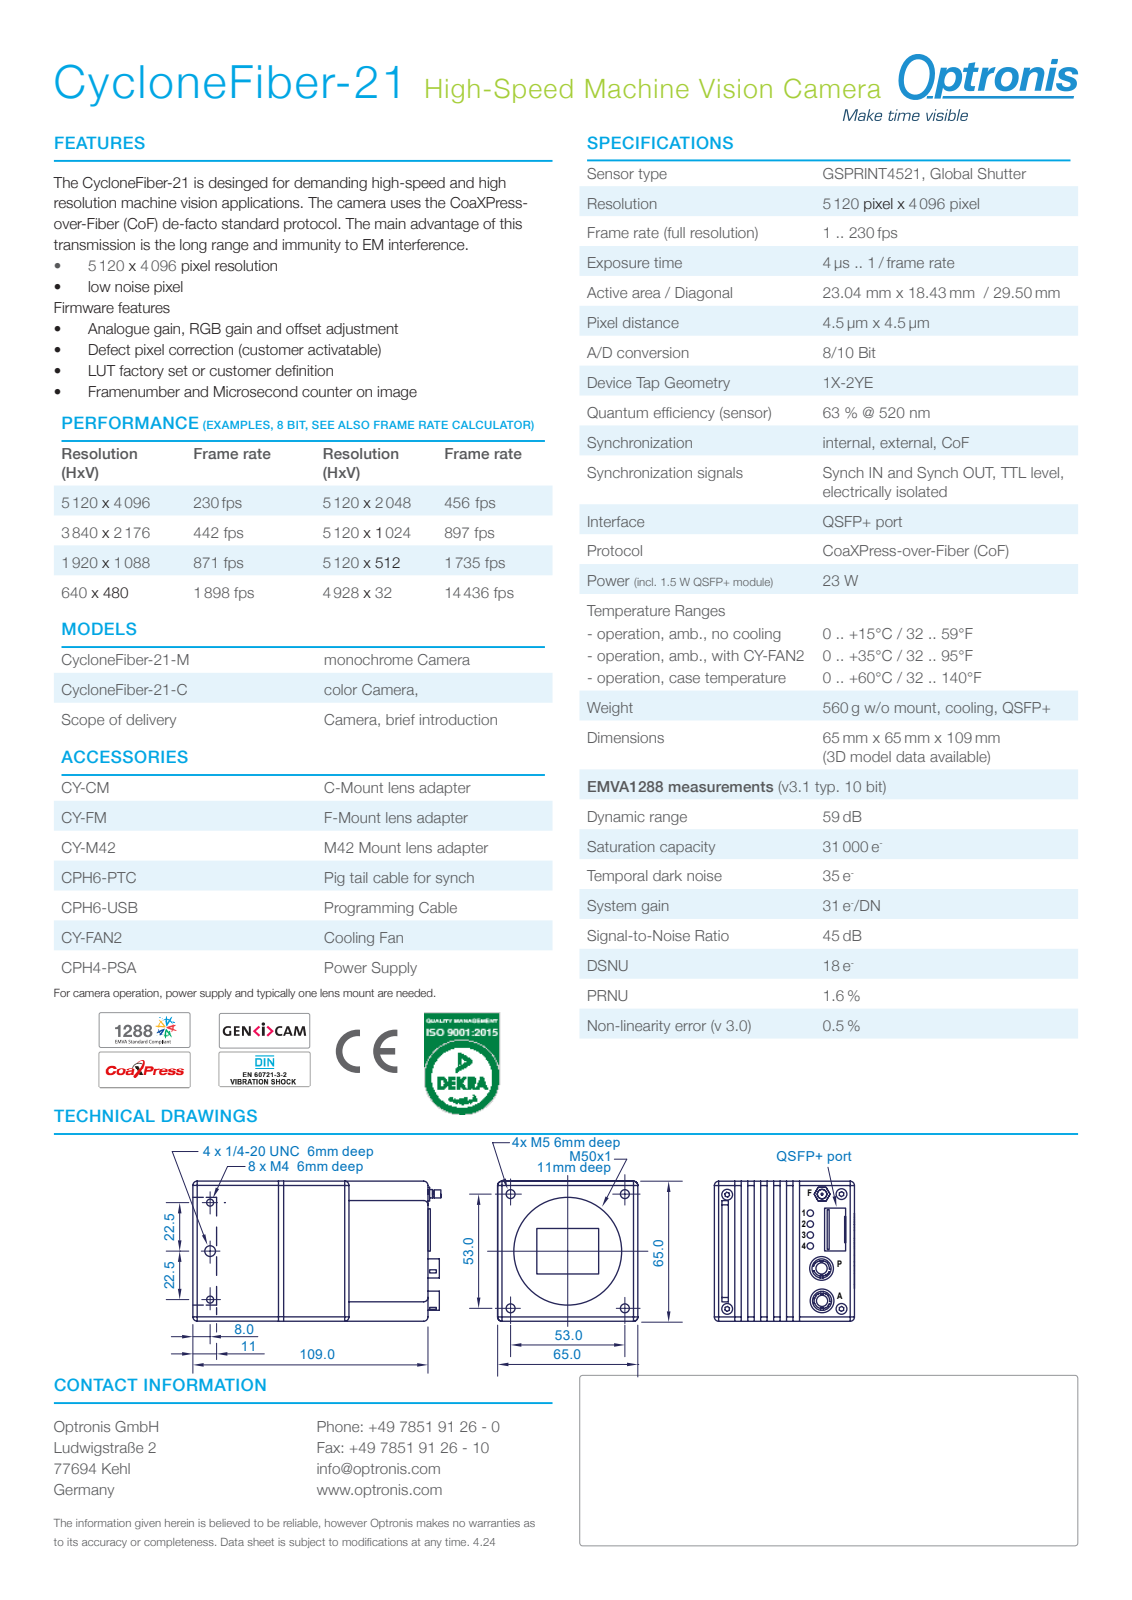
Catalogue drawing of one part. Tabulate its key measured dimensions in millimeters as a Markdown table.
| quantity | value |
| --- | --- |
| part name | 1200-MG-54_CycloneFiber_long |
| STEP written by | Autodesk Inventor 2026 (AUTOMOTIVE_DESIGN) |
| units | millimeters |
| bodies | 5 solids, 6476 faces (3119 planar, 2621 cylindrical, 736 other) |
| overall size | 108.59 × 65 × 65 |
| volume | 138 711 mm³ |
| surface area | 117 369 mm² |
| round holes (diameter × count) | 1 × 28, 0.8 × 16, 2.7 × 12, 0.5 × 10, 1.57 × 8, 2.01 × 4, 2.2 × 4, 2.85 × 4, 3.24 × 4, 4.2 × 4, 5 × 4, 5.5 × 4 |
| round bosses / shafts (diameter × count) | 0.97 × 438, 0.3 × 438, 1.1 × 12, 3.8 × 8, 2.5 × 8, 4.7 × 4, 4.5 × 4, 2.8 × 4 |
| partial cylindrical surfaces (radius × count) | 0.25 × 186, 0.2 × 60, 0.5 × 50, 0.1 × 45, 1 × 36, 2 × 34, 3 × 32, 0.13 × 28 |
| main face-to-face distances | 3, 6, 9, 12, 15, 18, 21, 24, 2, 63 |
| hole center spacings | 3.36, 7.83, 6.73, 12.7, 5, 10.97, 1.8, 7.2 |
